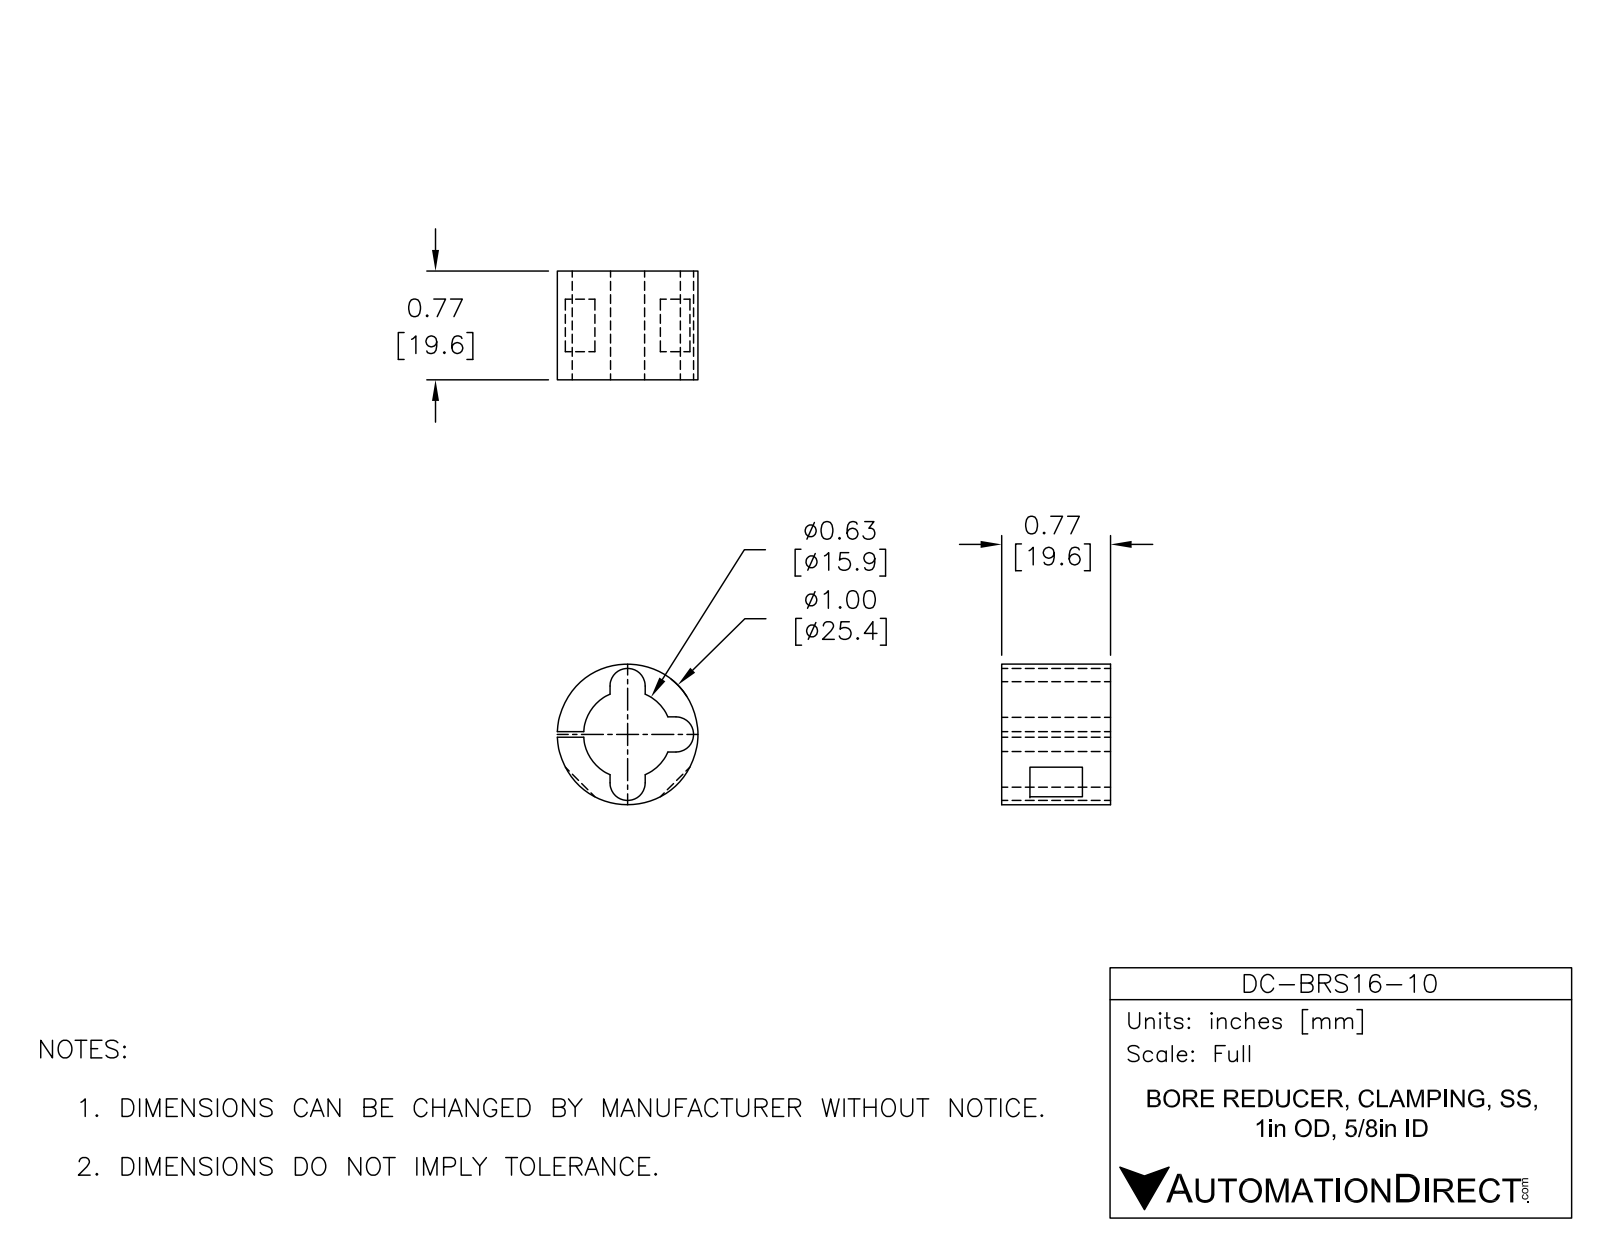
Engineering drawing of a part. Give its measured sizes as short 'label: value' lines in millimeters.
name: DC-BRS16-10
written by: SolidWorks 2015 (AUTOMOTIVE_DESIGN)
unit: mm
bodies: 1 solid, 27 faces (16 planar, 11 cylindrical, 0 other)
size: 25.4 × 25.39 × 19.63
volume: 4 599 mm³; area: 3 552 mm²
bosses: 1× ⌀25.4
rounds: 3× R3.17, 1× R7.94
face distances: 19.64, 1.02, 6.34, 2.66, 3.68, 5.08, 14.56, 9.48
